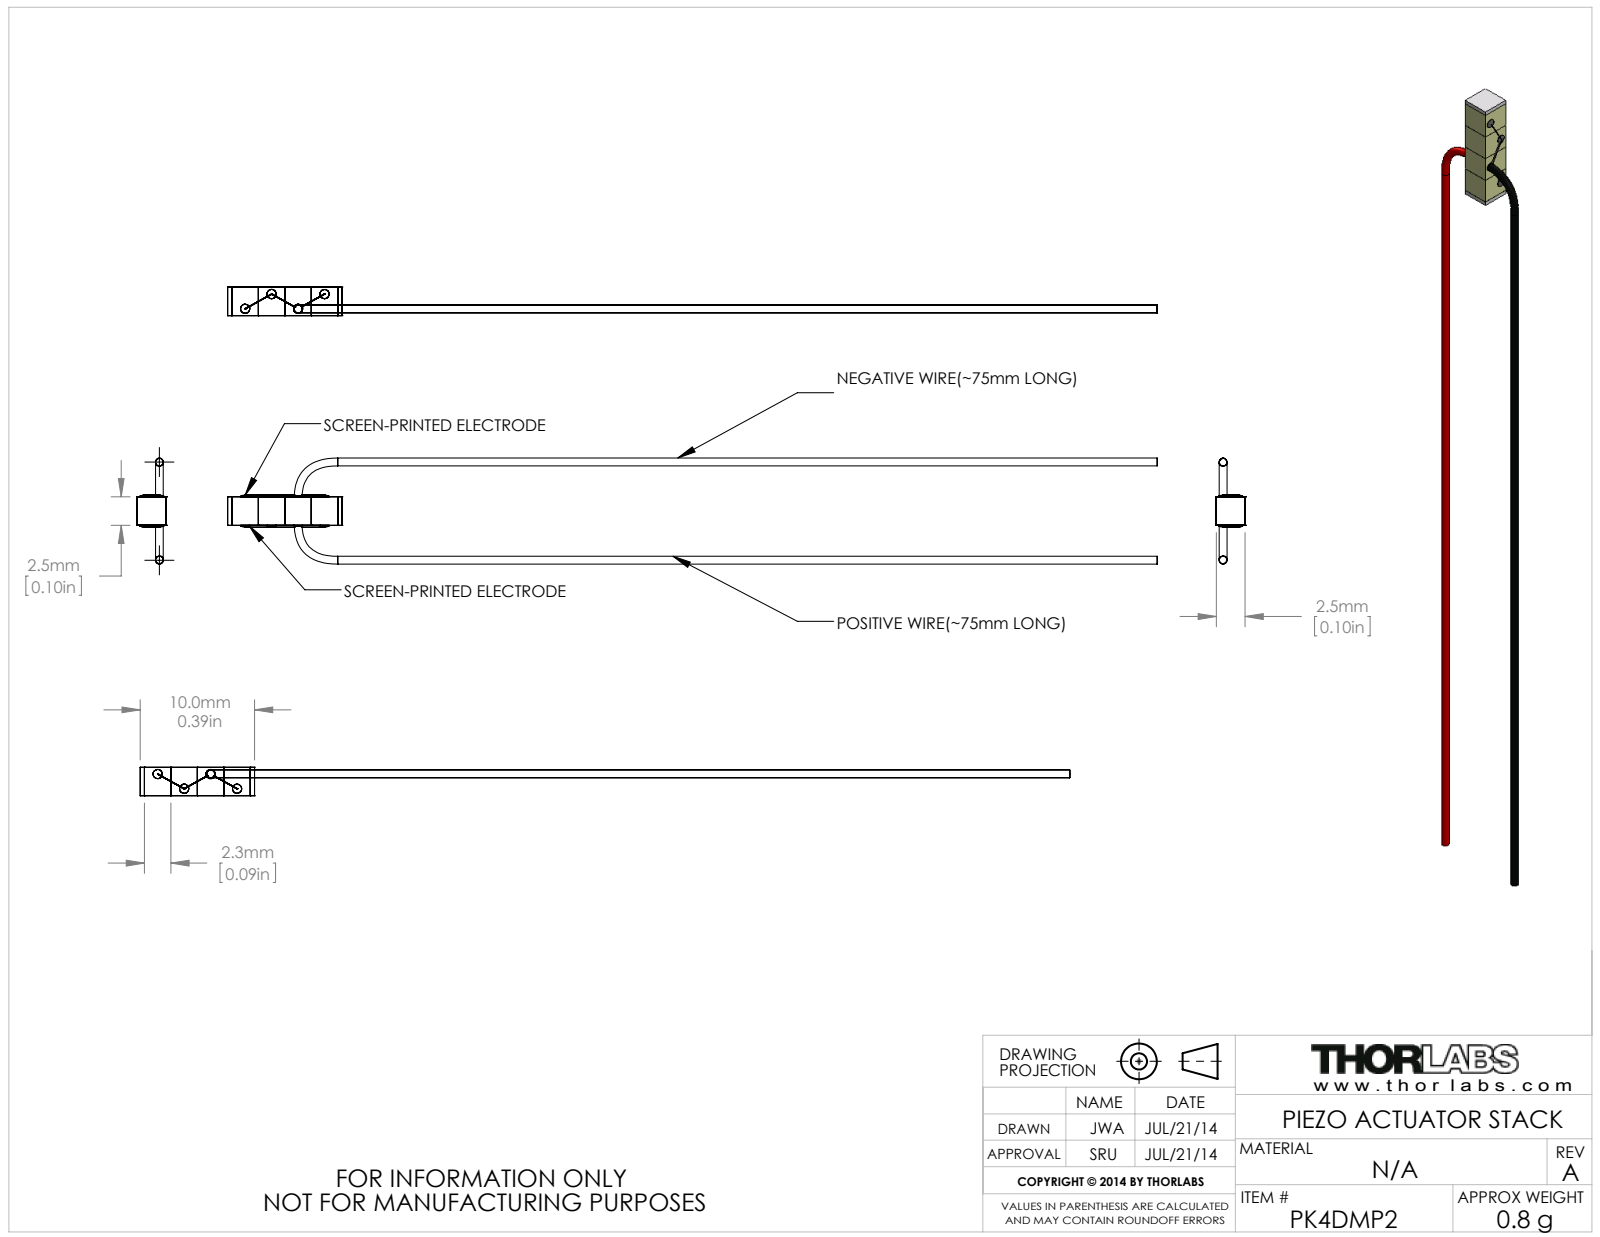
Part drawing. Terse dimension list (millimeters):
name: PK4DMP2
written by: SolidWorks 2012 (AUTOMOTIVE_DESIGN)
unit: mm
bodies: 3 solids, 132 faces (72 planar, 28 cylindrical, 32 other)
size: 81.15 × 9.25 × 2.5
volume: 118 mm³; area: 507 mm²
bosses: 4× ⌀0.8, 2× ⌀0.68
face distances: 2.5, 2.31, 4.62, 2.3, 2.32, 6.93, 4.61, 0.37, 9.61, 2.68
